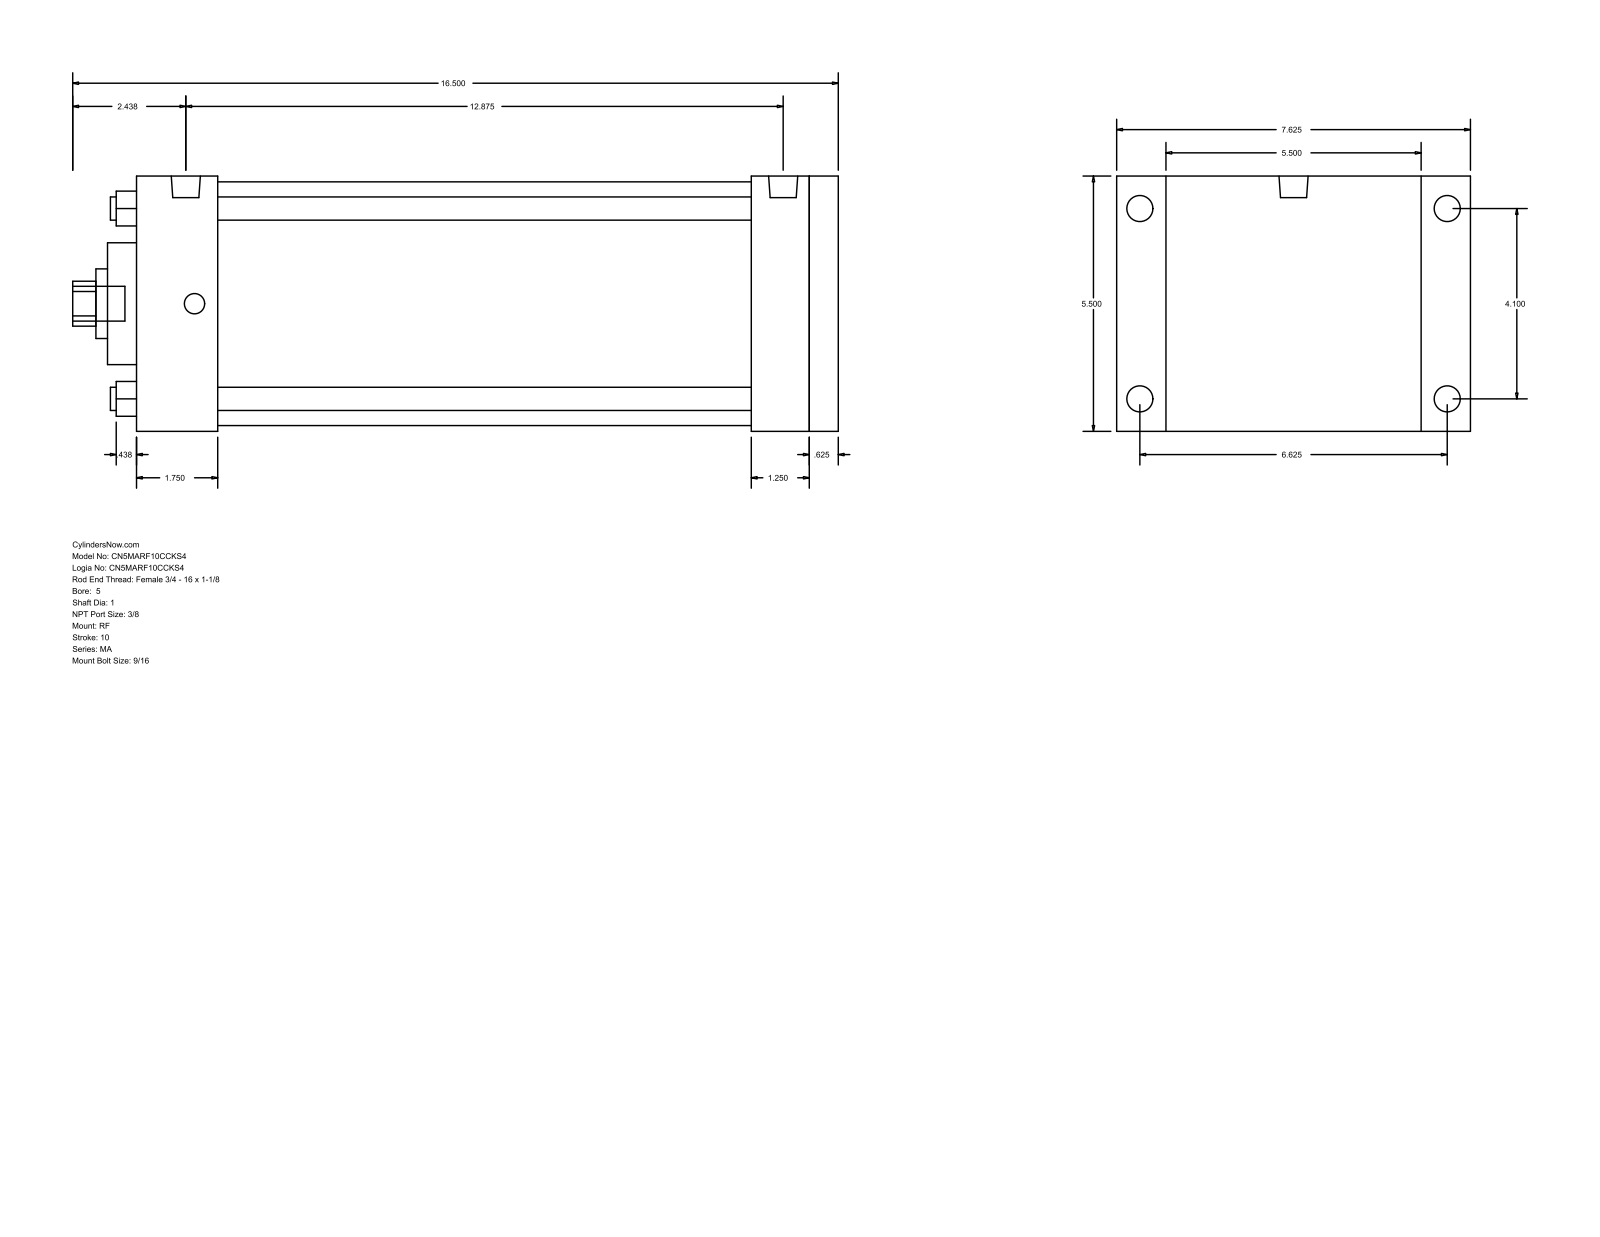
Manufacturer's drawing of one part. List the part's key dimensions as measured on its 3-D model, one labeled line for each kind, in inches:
Part name (STEP PRODUCT): MA_RF__0500_1
STEP written by: GSSL Pune (CONFIG_CONTROL_DESIGN)
Units: inches
Bodies: 0 solids, 94 faces (65 planar, 29 cylindrical, 0 other)
Overall size (bounding box): 16.5 × 7.625 × 5.5
Round holes (diameter × count): ⌀0.5 ×4, ⌀1 ×1, ⌀1.5 ×1, ⌀2.625 ×1, ⌀5.25 ×1
Round bosses / shafts (diameter × count): ⌀0.563 ×4, ⌀0.437 ×4, ⌀0.627 ×2, ⌀0.75 ×1
Partial cylindrical surfaces — rounded edges, fillets, slot ends (radius × count): R0.484 ×1
Main face-to-face distances: 5.5, 15.125, 0.625, 14.5, 1.75, 12.75, 13.375, 13.25, 11.5, 1.25
Hole centre spacings: 2.899, 4.1, 5.798
